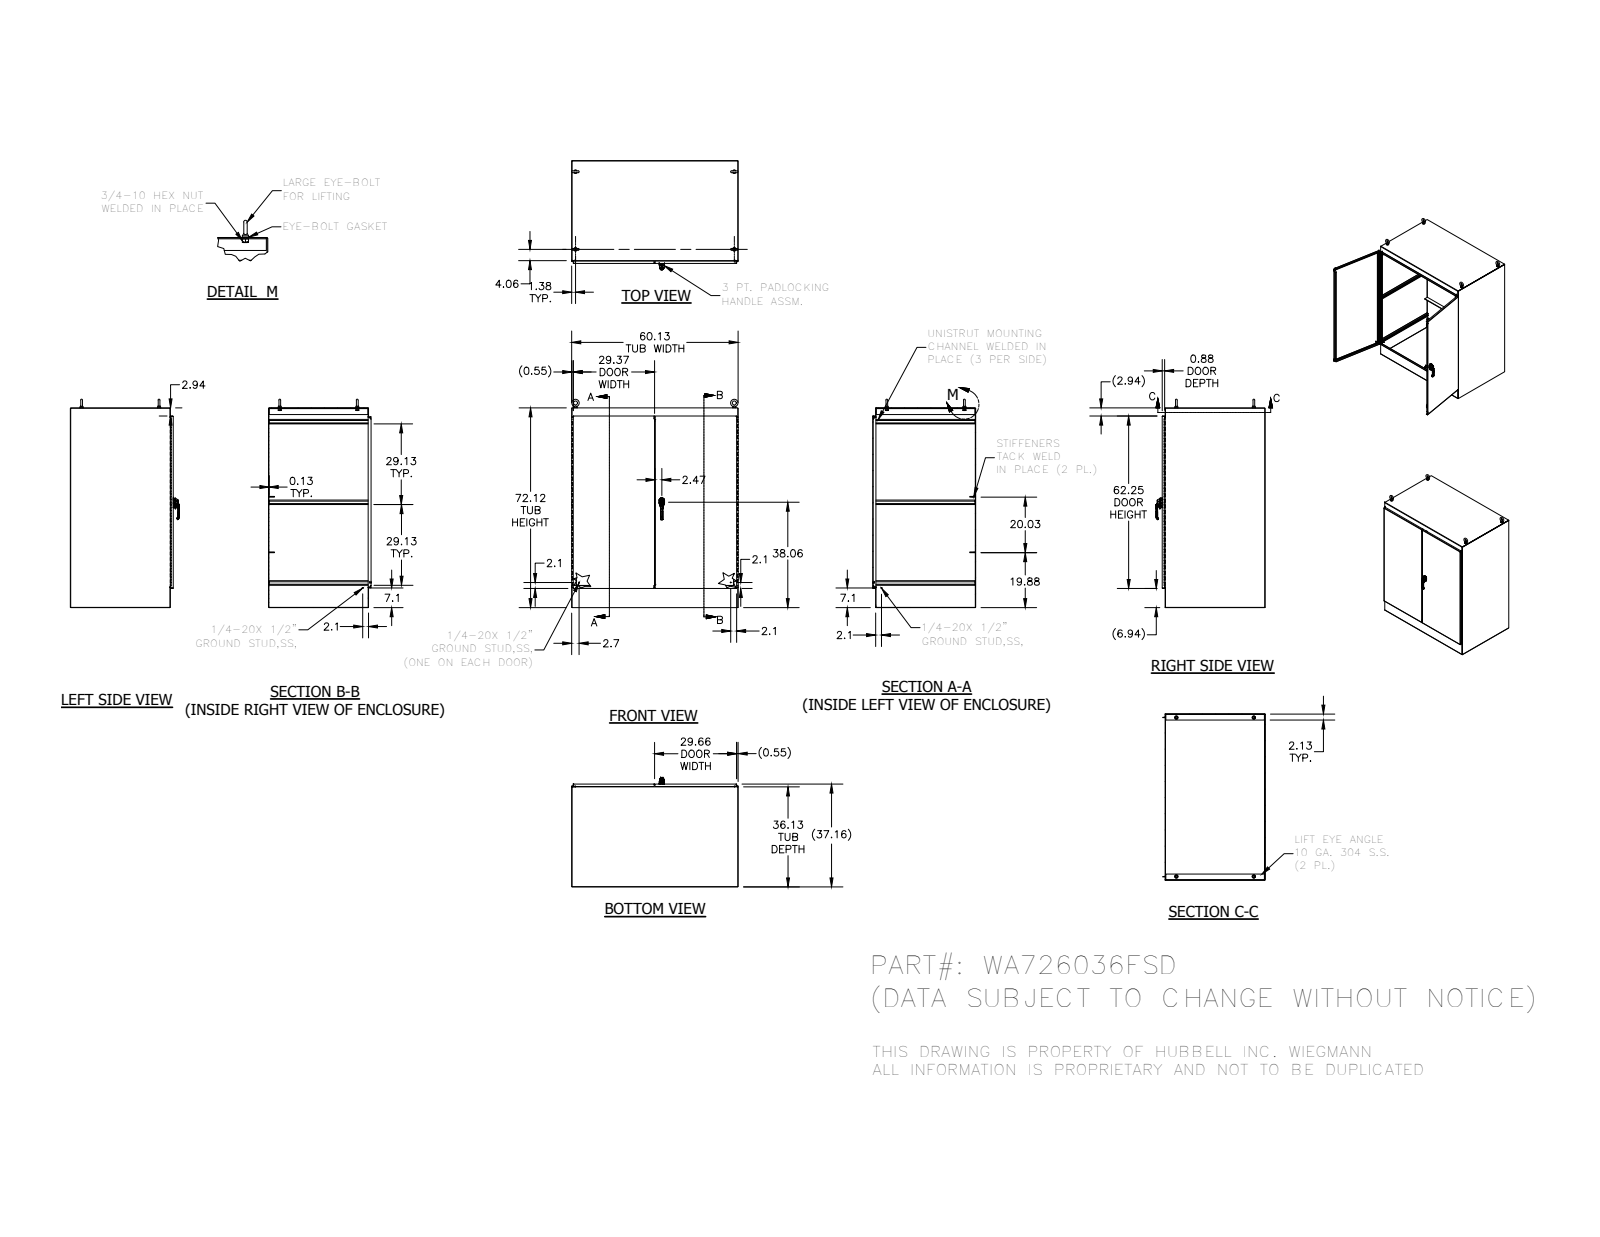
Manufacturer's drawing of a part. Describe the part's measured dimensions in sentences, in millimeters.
The part is named "FUN00105; HFW3025; 316298; 349132 (+8 more)". Its 3-D file was written by "Autodesk Inventor 2014 (AUTOMOTIVE_DESIGN)". It is 72 solids with 3928 faces: 1801 planar, 1295 cylindrical and 832 other. Overall it measures 1911.29 by 1527.54 by 1001.56 millimeters. Its volume is 43 260 000 cubic millimeters and its surface area 27 340 000 square millimeters. Round holes: 8 of diameter 7.02, 4 of diameter 5.08, 4 of diameter 16.31, 4 of diameter 20.64, 3 of diameter 5.4, 3 of diameter 6, 3 of diameter 7.11, 2 of diameter 3.17, 2 of diameter 6.13, 2 of diameter 6.35, 2 of diameter 6.41, 2 of diameter 10.16. Round bosses or shafts: 5 of diameter 6.35, 4 of diameter 31.75, 4 of diameter 28.45, 4 of diameter 19.05, 3 of diameter 8.56, 2 of diameter 25.4, 2 of diameter 14.29, 2 of diameter 13.37. Partial cylindrical surfaces (rounded edges, fillets, slot ends): 164 of radius 0.5, 84 of radius 0.3, 24 of radius 0.79, 21 of radius 3.97, 19 of radius 0.47, 16 of radius 0.25, 15 of radius 2, 14 of radius 1.27. The main face-to-face distances are 3.18, 1524, 1828.8, 3.17, 940.77, 937.59, 943.94, 940.76, 1520.82, 1527.18. The hole center spacings are 6, 6.5, 9.67, 9.69, 9.72, 12.49, 12.5, 19.36.
